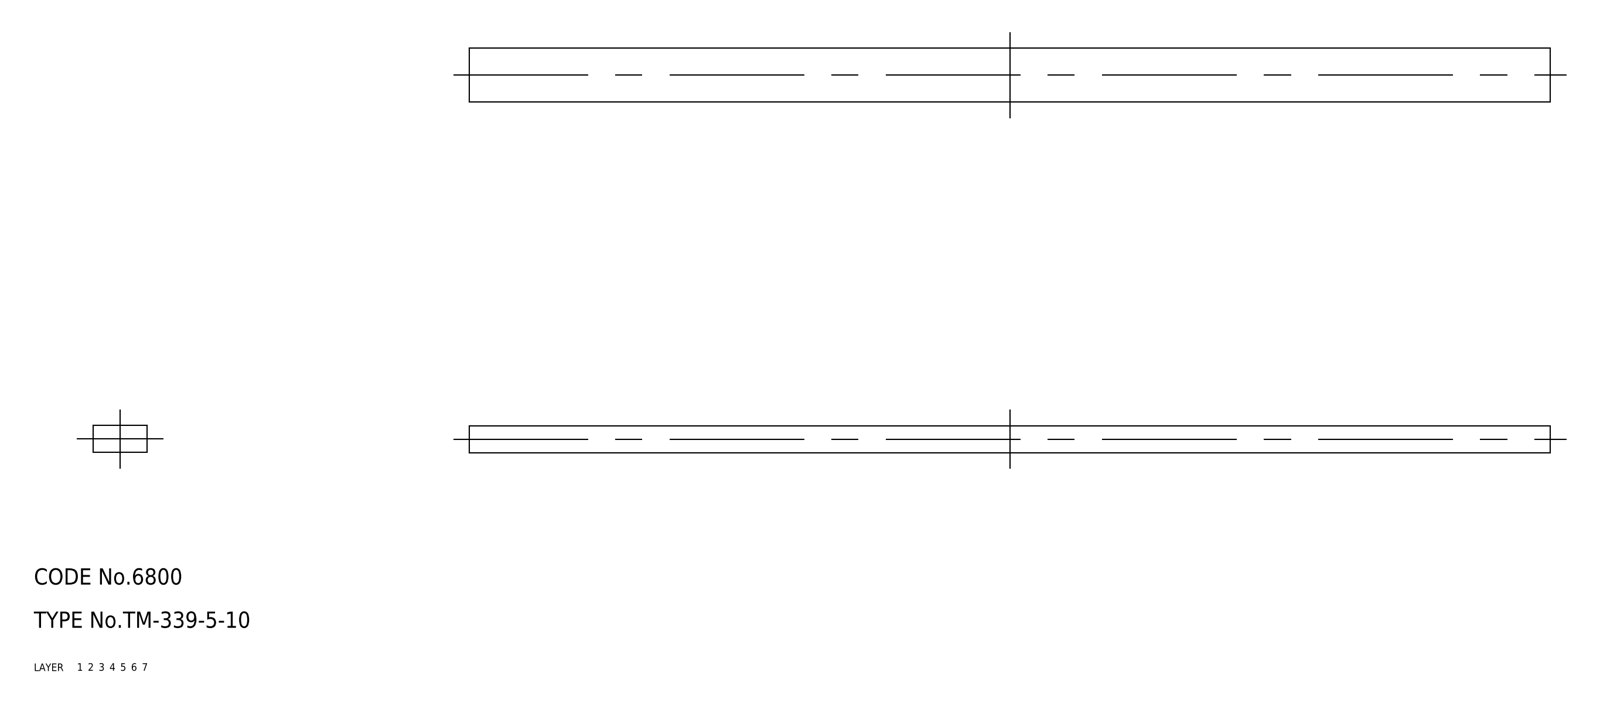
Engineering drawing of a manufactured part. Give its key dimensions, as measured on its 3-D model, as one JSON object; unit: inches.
{"part_name": "rubber foam; TM_339_5_10", "step_written_by": "SolidWorks 2015 (AUTOMOTIVE_DESIGN)", "units": "inches", "bodies": {"solids": 1, "faces": 6, "planar": 6, "cylindrical": 0, "other": 0}, "overall_size": [7.874, 0.394, 0.197], "volume_in3": 0.61, "surface_area_in2": 9.455, "face_to_face_distances": [0.197, 0.394, 7.874]}
